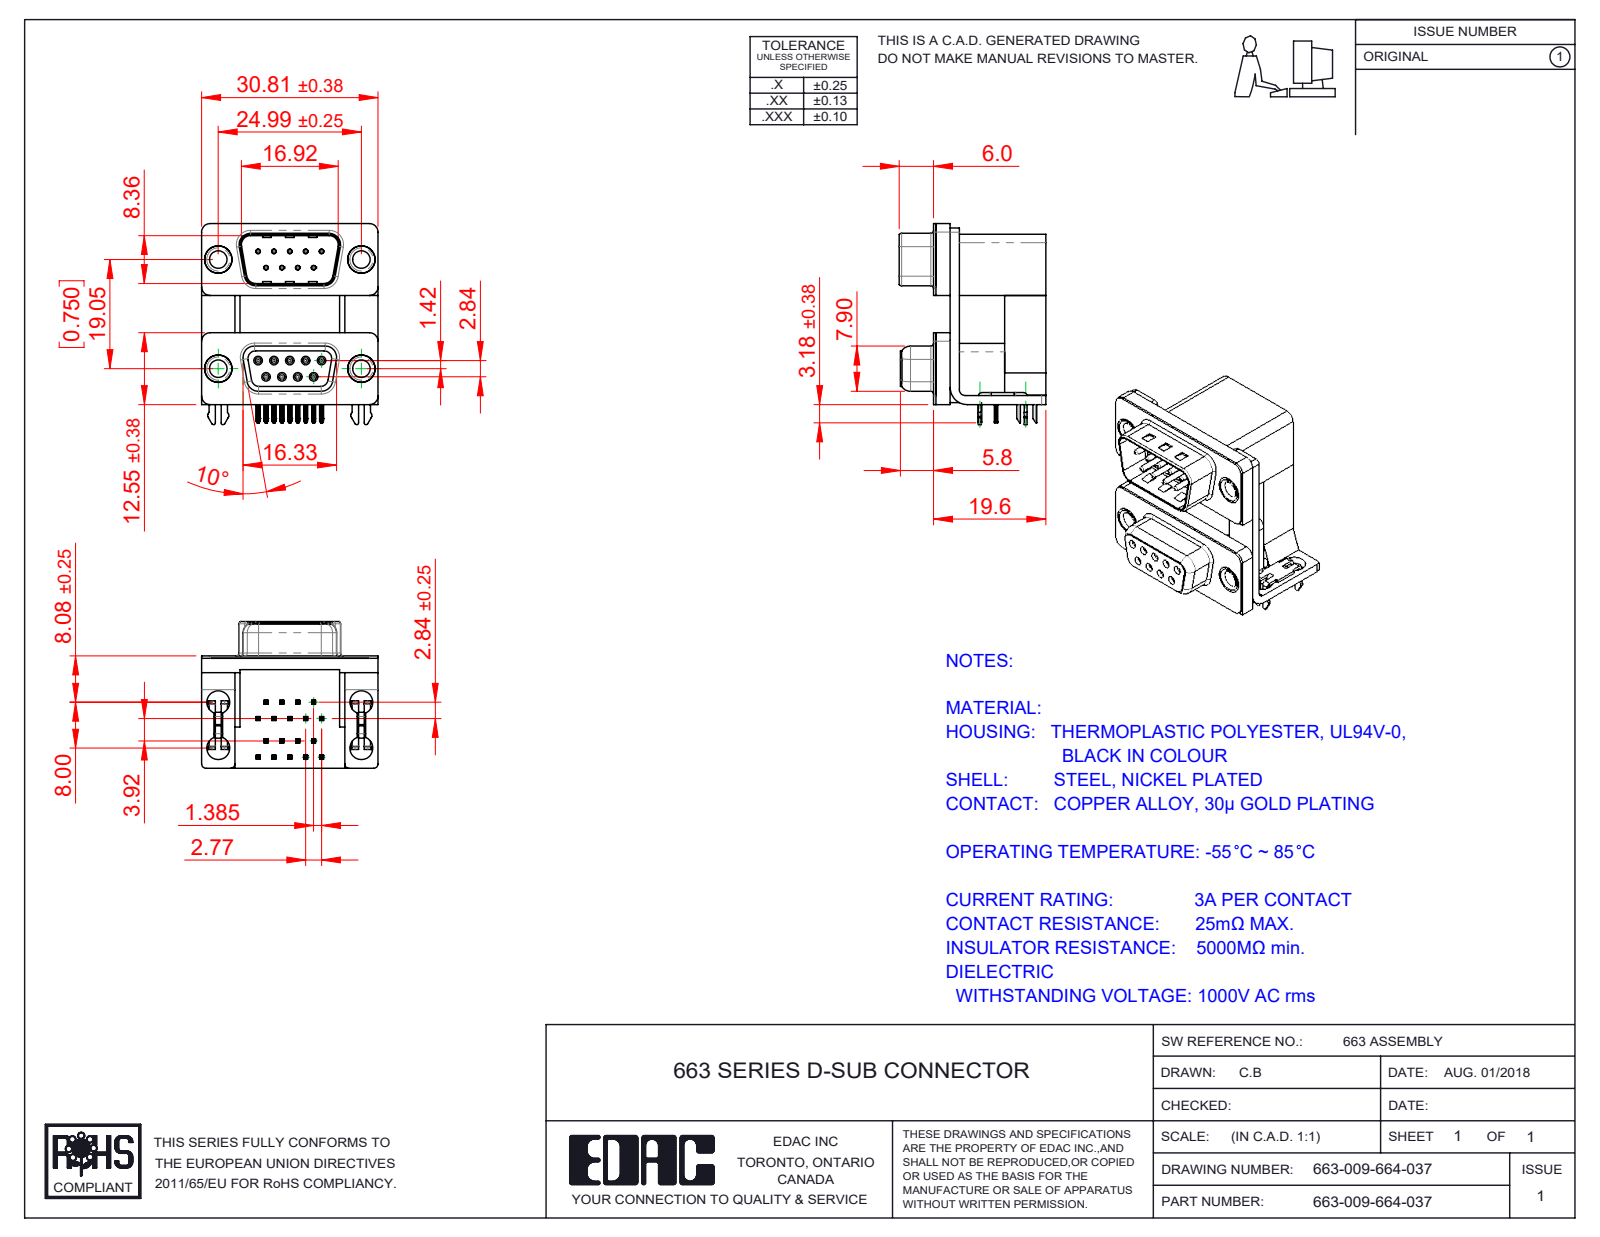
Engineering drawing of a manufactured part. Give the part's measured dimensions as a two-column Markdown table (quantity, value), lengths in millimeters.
| quantity | value |
| --- | --- |
| part name | 663 Contact Bottom Upper_M; 663 Mounting Bracket_2ProngM; 663 Contact Top Upper_M; 663 Contact Bottom Lower (+8 more) |
| STEP written by | SolidWorks 2020 (CONFIG_CONTROL_DESIGN) |
| units | millimeters |
| bodies | 31 solids, 2597 faces (1365 planar, 709 cylindrical, 523 other) |
| overall size | 35.1 × 30.81 × 25.6 |
| volume | 10 795 mm³ |
| surface area | 12 692 mm² |
| round holes (diameter × count) | 0.8 × 18, 0.35 × 9, 0.9 × 9, 4 × 8, 3.05 × 4, 3.5 × 4, 4.8 × 4, 5 × 4 |
| round bosses / shafts (diameter × count) | 1.2 × 9, 0.75 × 9, 4.9 × 4, 4.75 × 4, 3.85 × 4 |
| partial cylindrical surfaces (radius × count) | 0.1 × 74, 0.25 × 46, 0.15 × 36, 0.12 × 18, 0.35 × 18, 0.5 × 16, 1.5 × 15, 0.75 × 10 |
| main face-to-face distances | 0.4, 2.5, 16.7, 19.2, 9.5, 7.2, 12, 1.6, 19.6, 12.4 |
| hole center spacings | 3.16, 2.77, 19.25, 19.05, 5.54, 19.84, 16.27, 21.93 |
